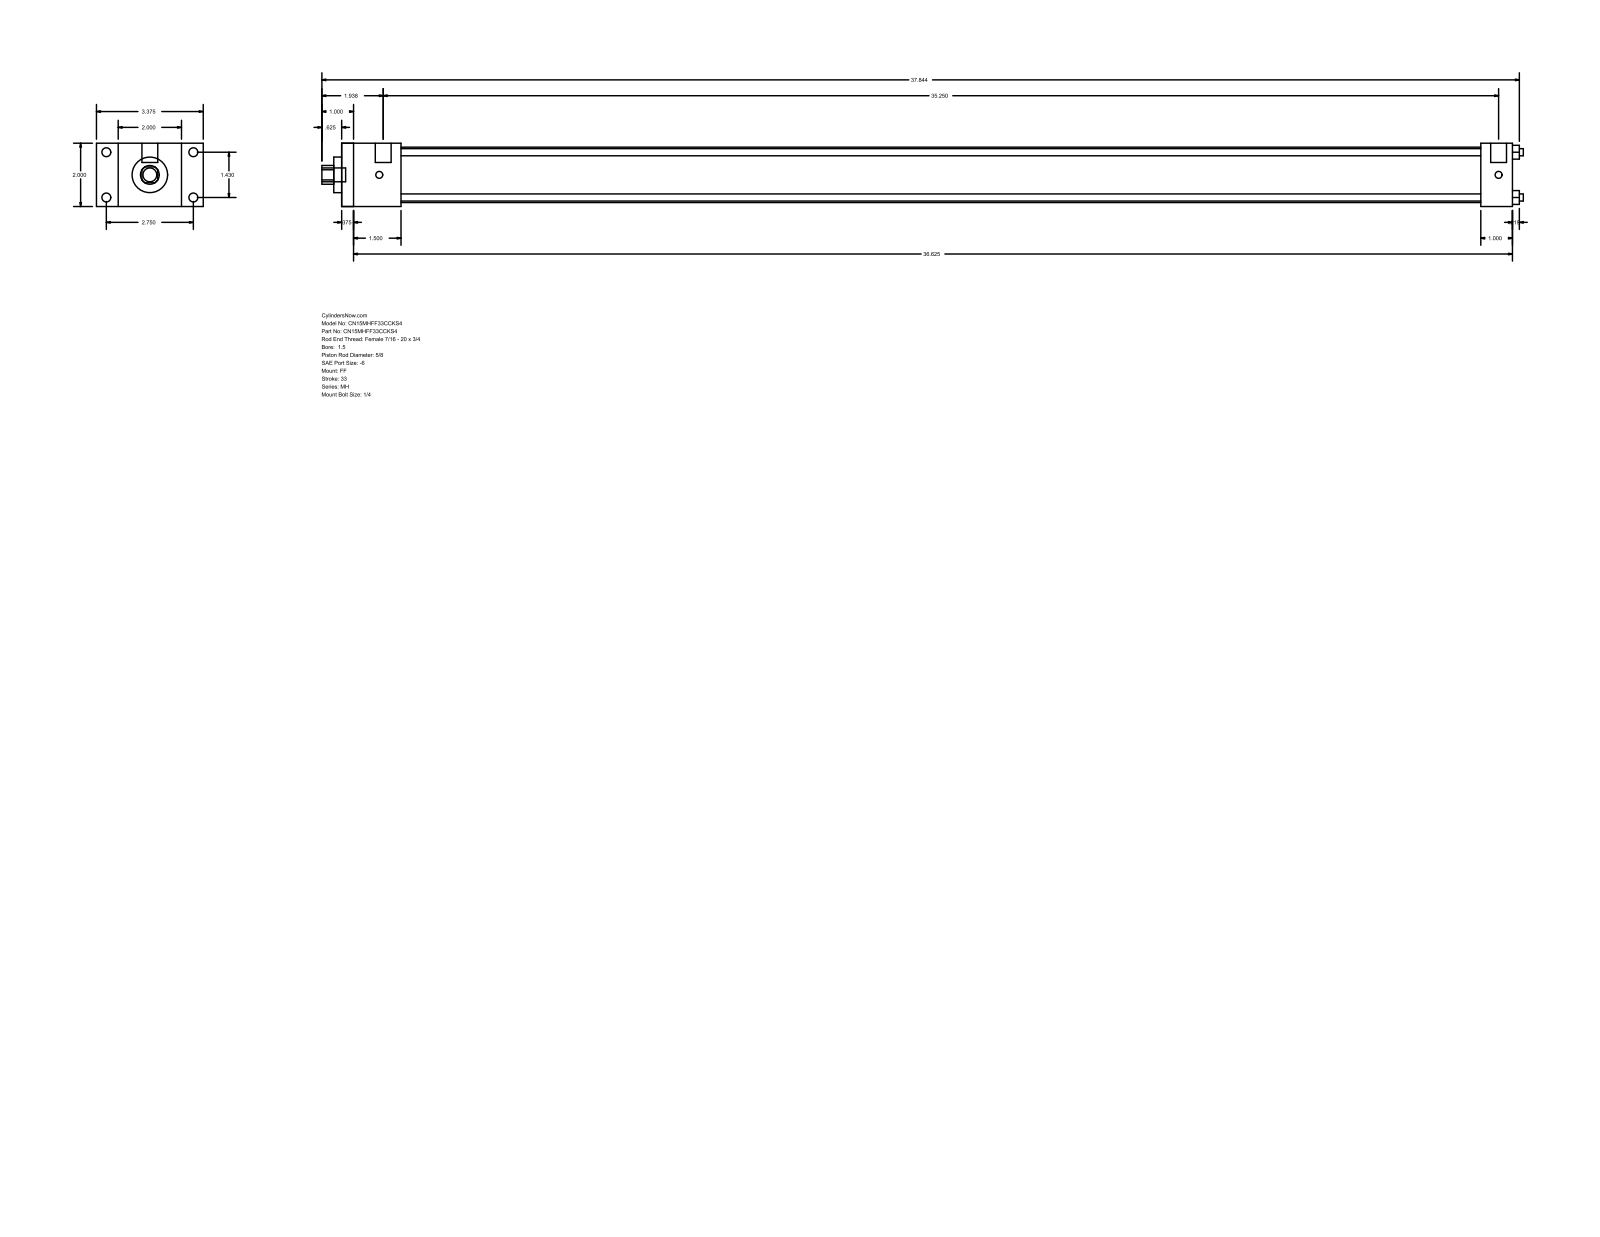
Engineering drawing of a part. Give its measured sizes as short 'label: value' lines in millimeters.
name: MH_FF__0150_0.625
written by: GSSL Pune (CONFIG_CONTROL_DESIGN)
unit: mm
bodies: 0 solids, 92 faces (64 planar, 28 cylindrical, 0 other)
size: 964.41 × 85.72 × 50.8
holes: 4× ⌀5.71, 1× ⌀15.88, 1× ⌀28.57, 1× ⌀44.45
bosses: 4× ⌀7.14, 4× ⌀5.56, 2× ⌀12.7, 1× ⌀11.11
rounds: 1× R7.54
face distances: 50.8, 939.79, 9.52, 930.27, 25.4, 17.46, 68.26, 47.62, 38.1, 892.17
hole spacings: 25.68, 36.32, 51.36
